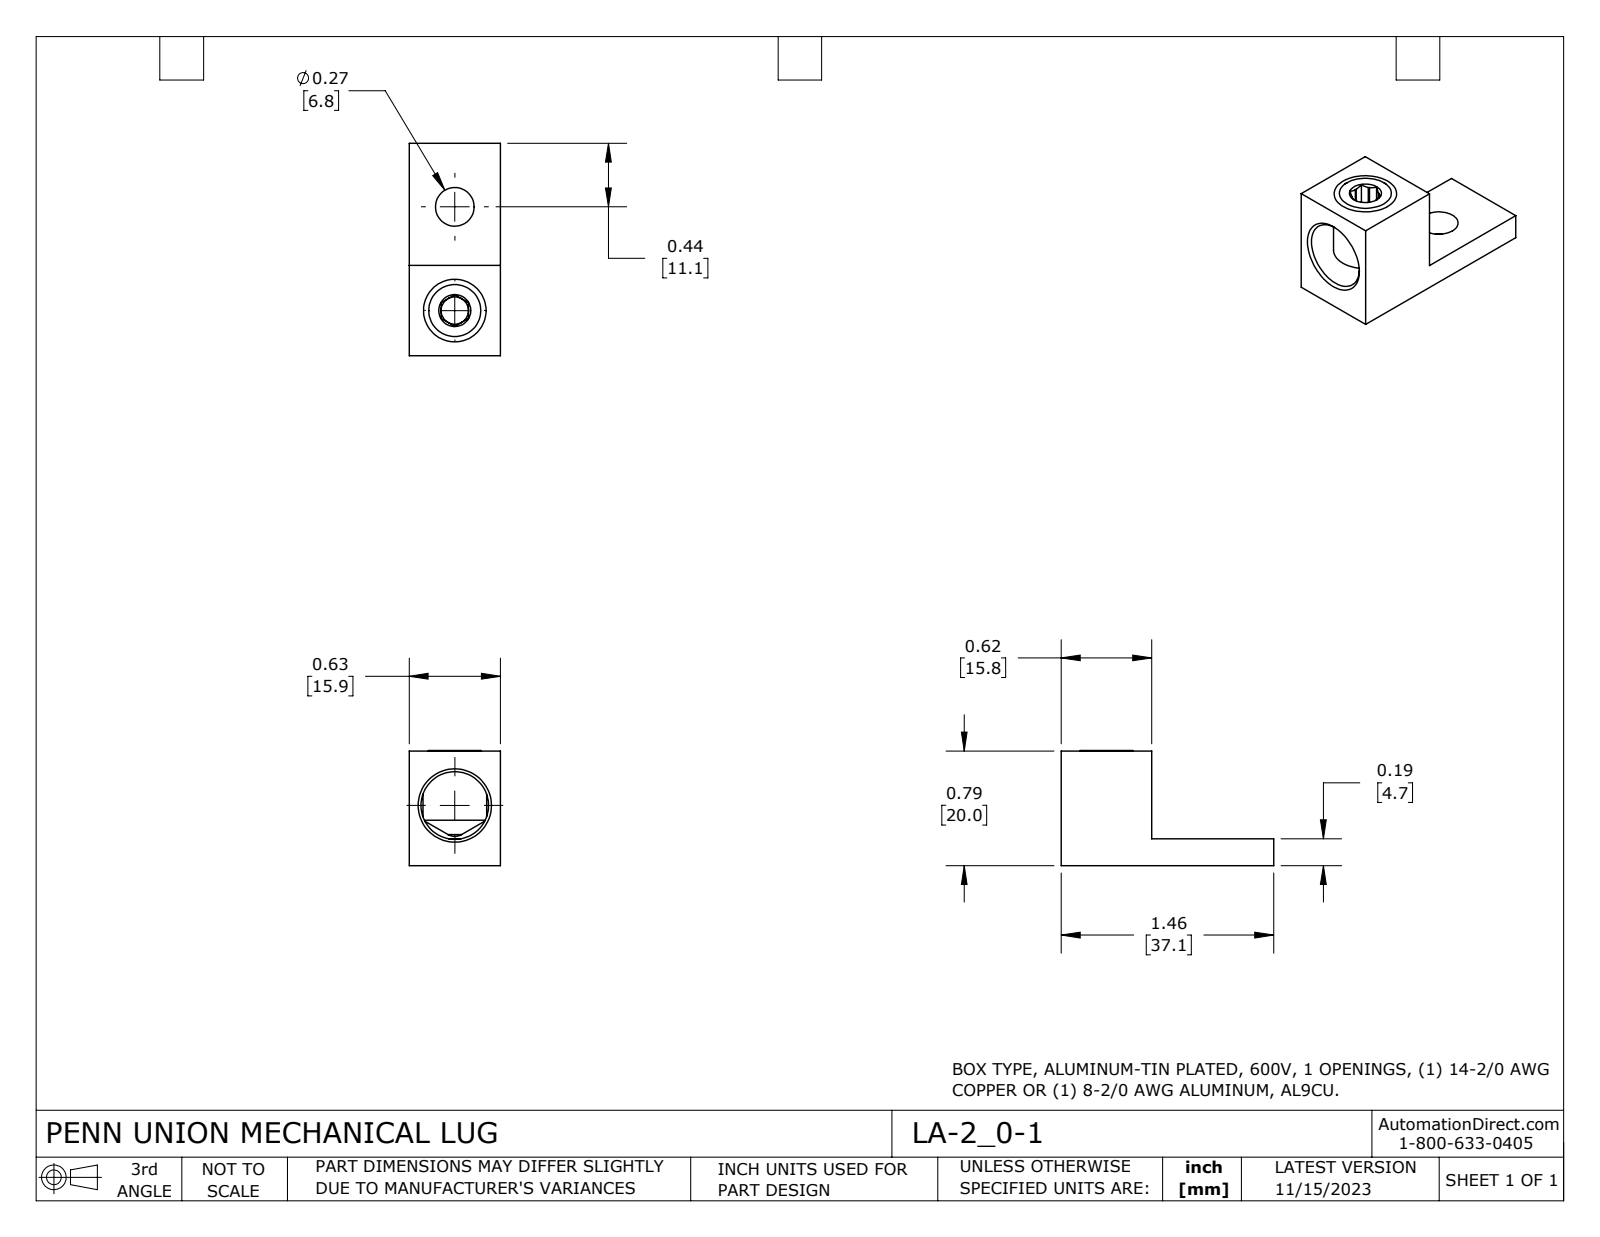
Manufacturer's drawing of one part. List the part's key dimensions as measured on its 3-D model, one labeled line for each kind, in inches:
Part name (STEP PRODUCT): LA-2_0-1
STEP written by: SolidWorks 2023 (CONFIG_CONTROL_DESIGN)
Units: inches
Bodies: 2 solids, 51 faces (28 planar, 10 cylindrical, 13 other)
Overall size (bounding box): 1.461 × 0.792 × 0.626
Volume: 0.334 in³ · Surface area: 5.841 in²
Round holes (diameter × count): ⌀0.188 ×1, ⌀0.266 ×1, ⌀0.391 ×1, ⌀0.465 ×1
Round bosses / shafts (diameter × count): ⌀0.437 ×1
Main face-to-face distances: 0.626, 0.185, 0.787, 0.602, 0.622, 1.461, 0.839, 0.792, 0.607, 0.219
Hole centre spacings: 0.713
